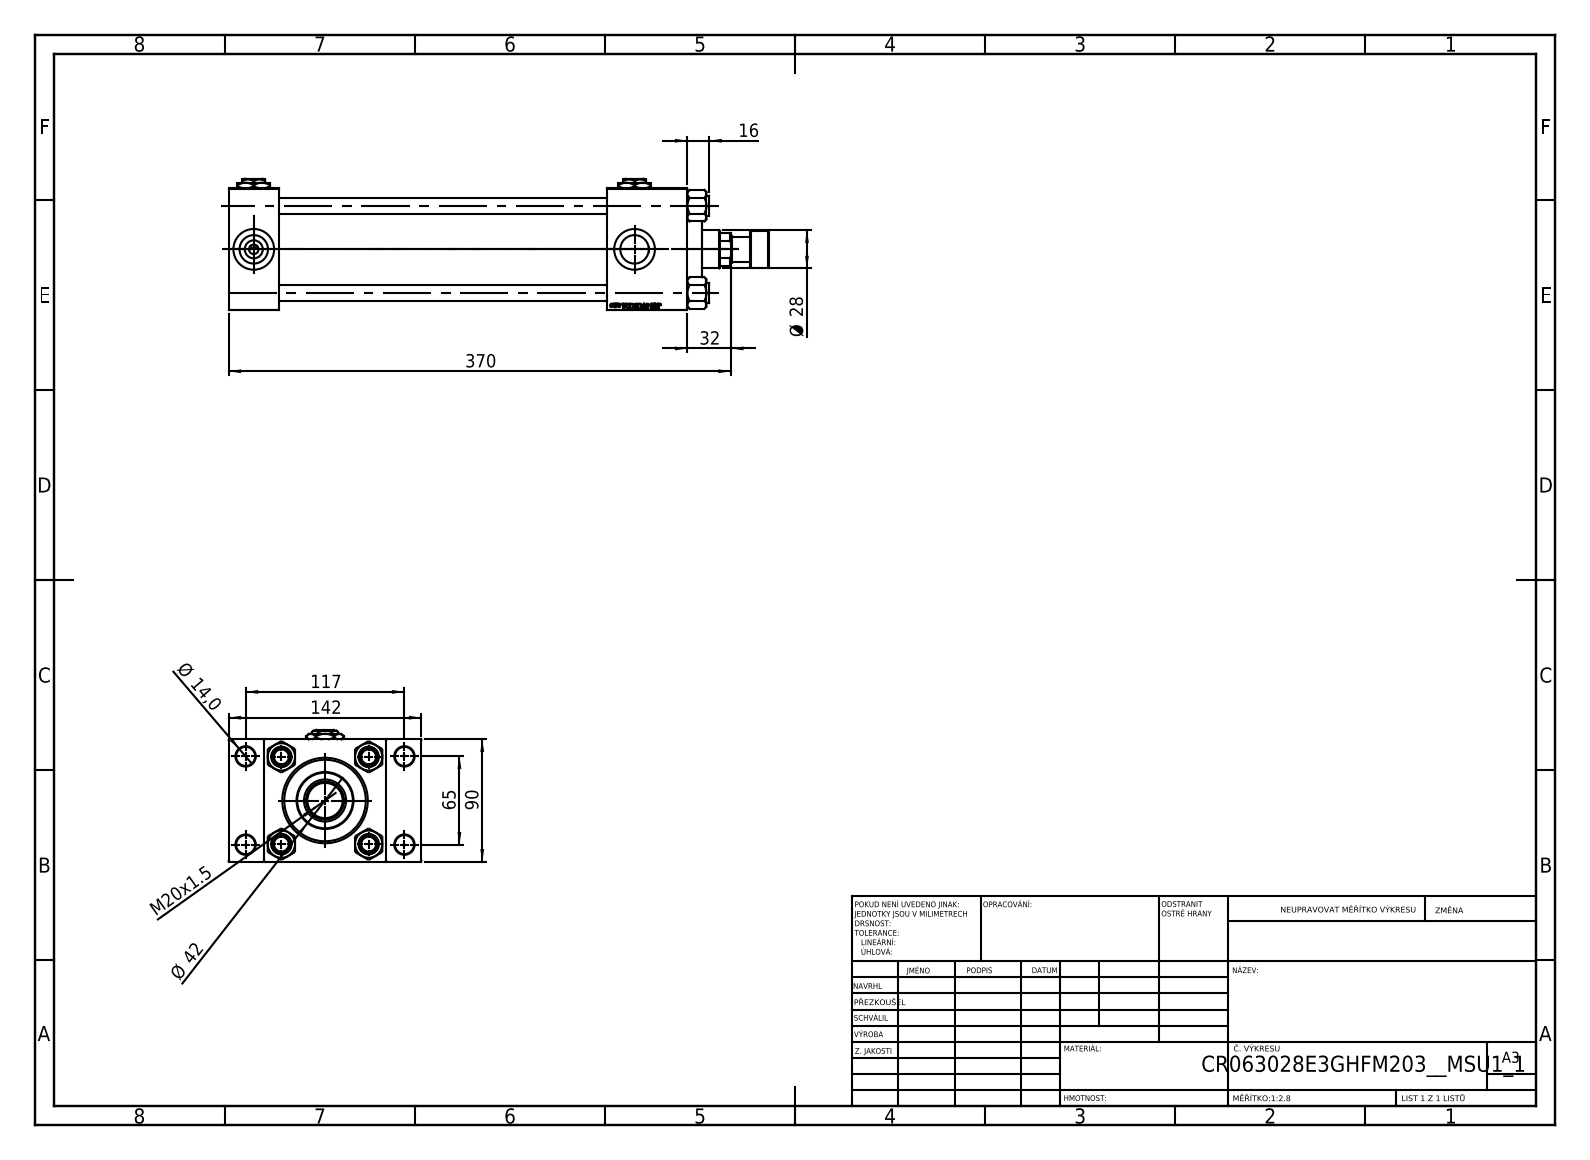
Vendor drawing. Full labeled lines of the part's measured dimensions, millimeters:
Part name (STEP PRODUCT): NUT_M5_E; V215CR_VCP_E; V215_VC_A; V215CR_ROD_END_F (+3 more)
STEP written by: SolidWorks 2019 (CONFIG_CONTROL_DESIGN)
Units: millimetres
Bodies: 14 solids, 1251 faces (550 planar, 101 cylindrical, 600 other)
Overall size (bounding box): 398 × 142 × 97
Volume: 1 419 000 mm³ · Surface area: 334 251 mm²
Round holes (diameter × count): ⌀12 ×4, ⌀14 ×4, ⌀20.96 ×4, ⌀30 ×4, ⌀7 ×3, ⌀18.5 ×1, ⌀28 ×1, ⌀31 ×1, ⌀50 ×1, ⌀60 ×1, ⌀63 ×1
Round bosses / shafts (diameter × count): ⌀15 ×4, ⌀69 ×1, ⌀42 ×1, ⌀27 ×1, ⌀18 ×1
Main face-to-face distances: 90, 37, 338, 301, 26, 116, 59, 279, 242, 309.3
Hole centre spacings: 26.35, 45.47, 64.3, 66.92, 69.81, 90.65, 111.34, 65
